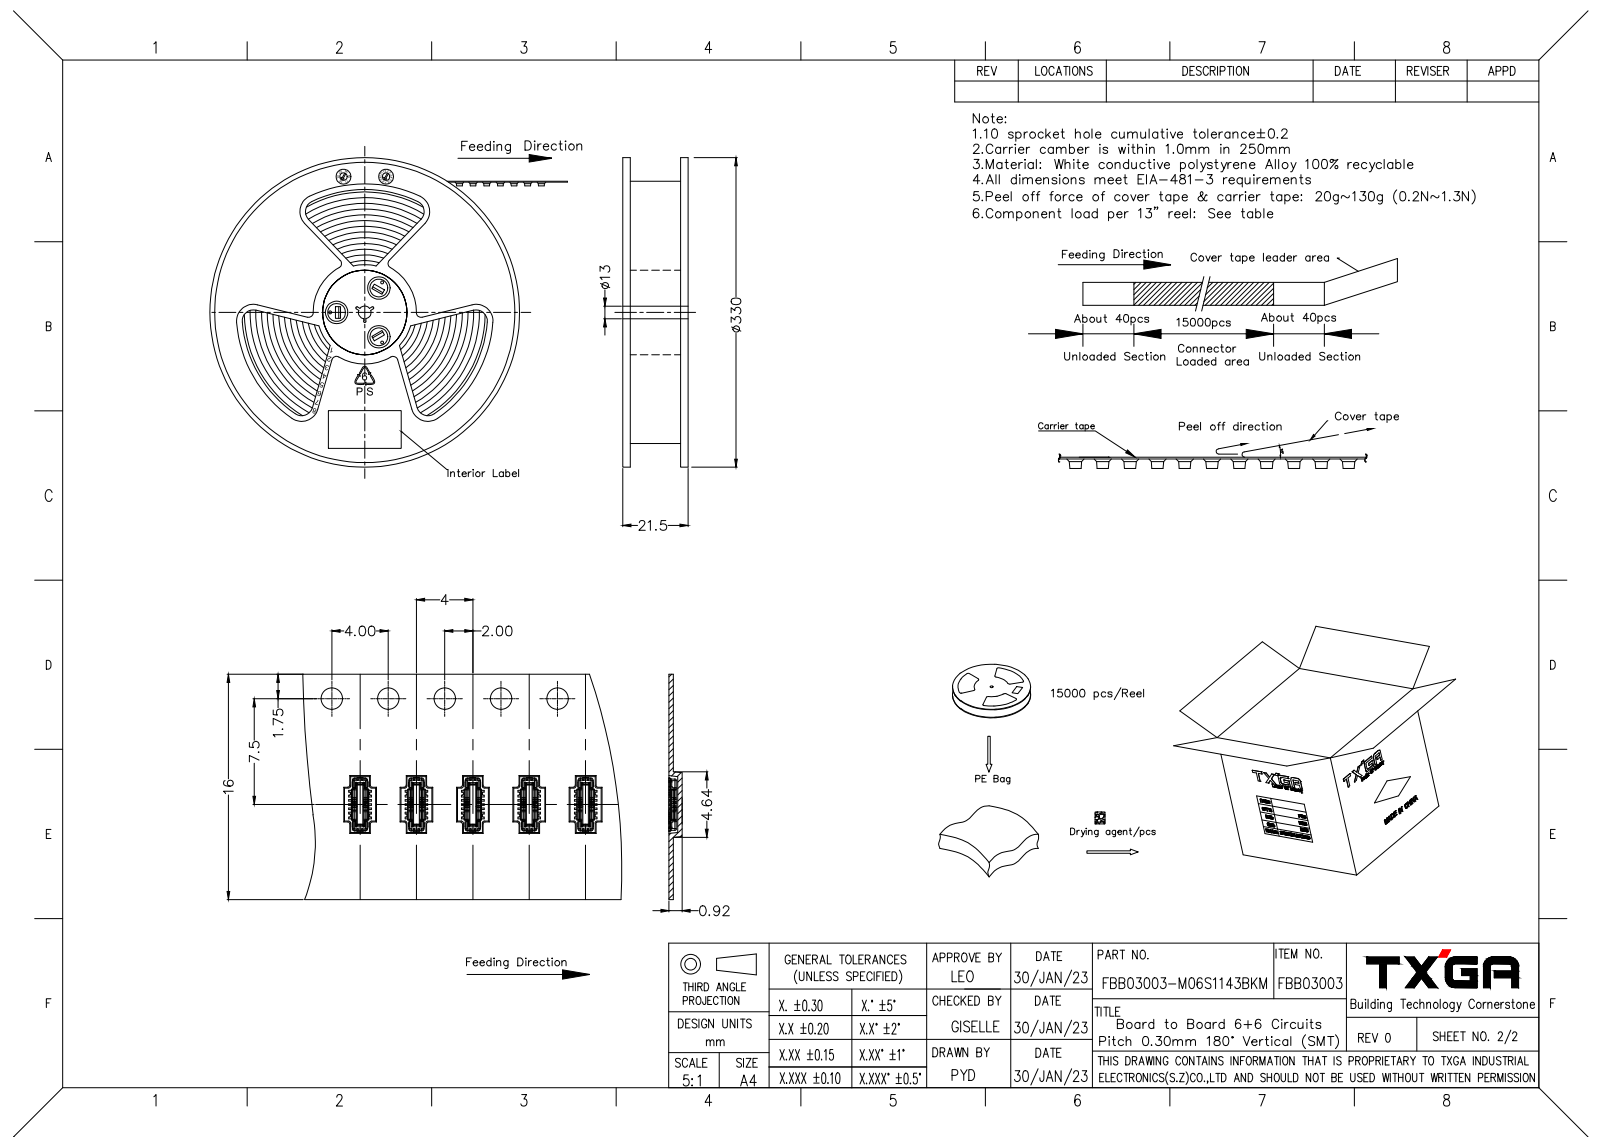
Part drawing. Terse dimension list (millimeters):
name: PRT0001
written by: CREO PARAMETRIC BY PTC INC, 2019010 (AUTOMOTIVE_DESIGN)
unit: mm
bodies: 1 solid, 248 faces (168 planar, 56 cylindrical, 24 other)
size: 3.94 × 1.9 × 0.49
volume: 1 mm³; area: 16 mm²
rounds: 10× R0.1, 4× R0.12, 4× R0.15, 4× R0.18, 2× R0.11
face distances: 0.78, 0.52, 0.42, 0.74, 1, 0.49, 1.04, 0.43, 1.06, 1.02
